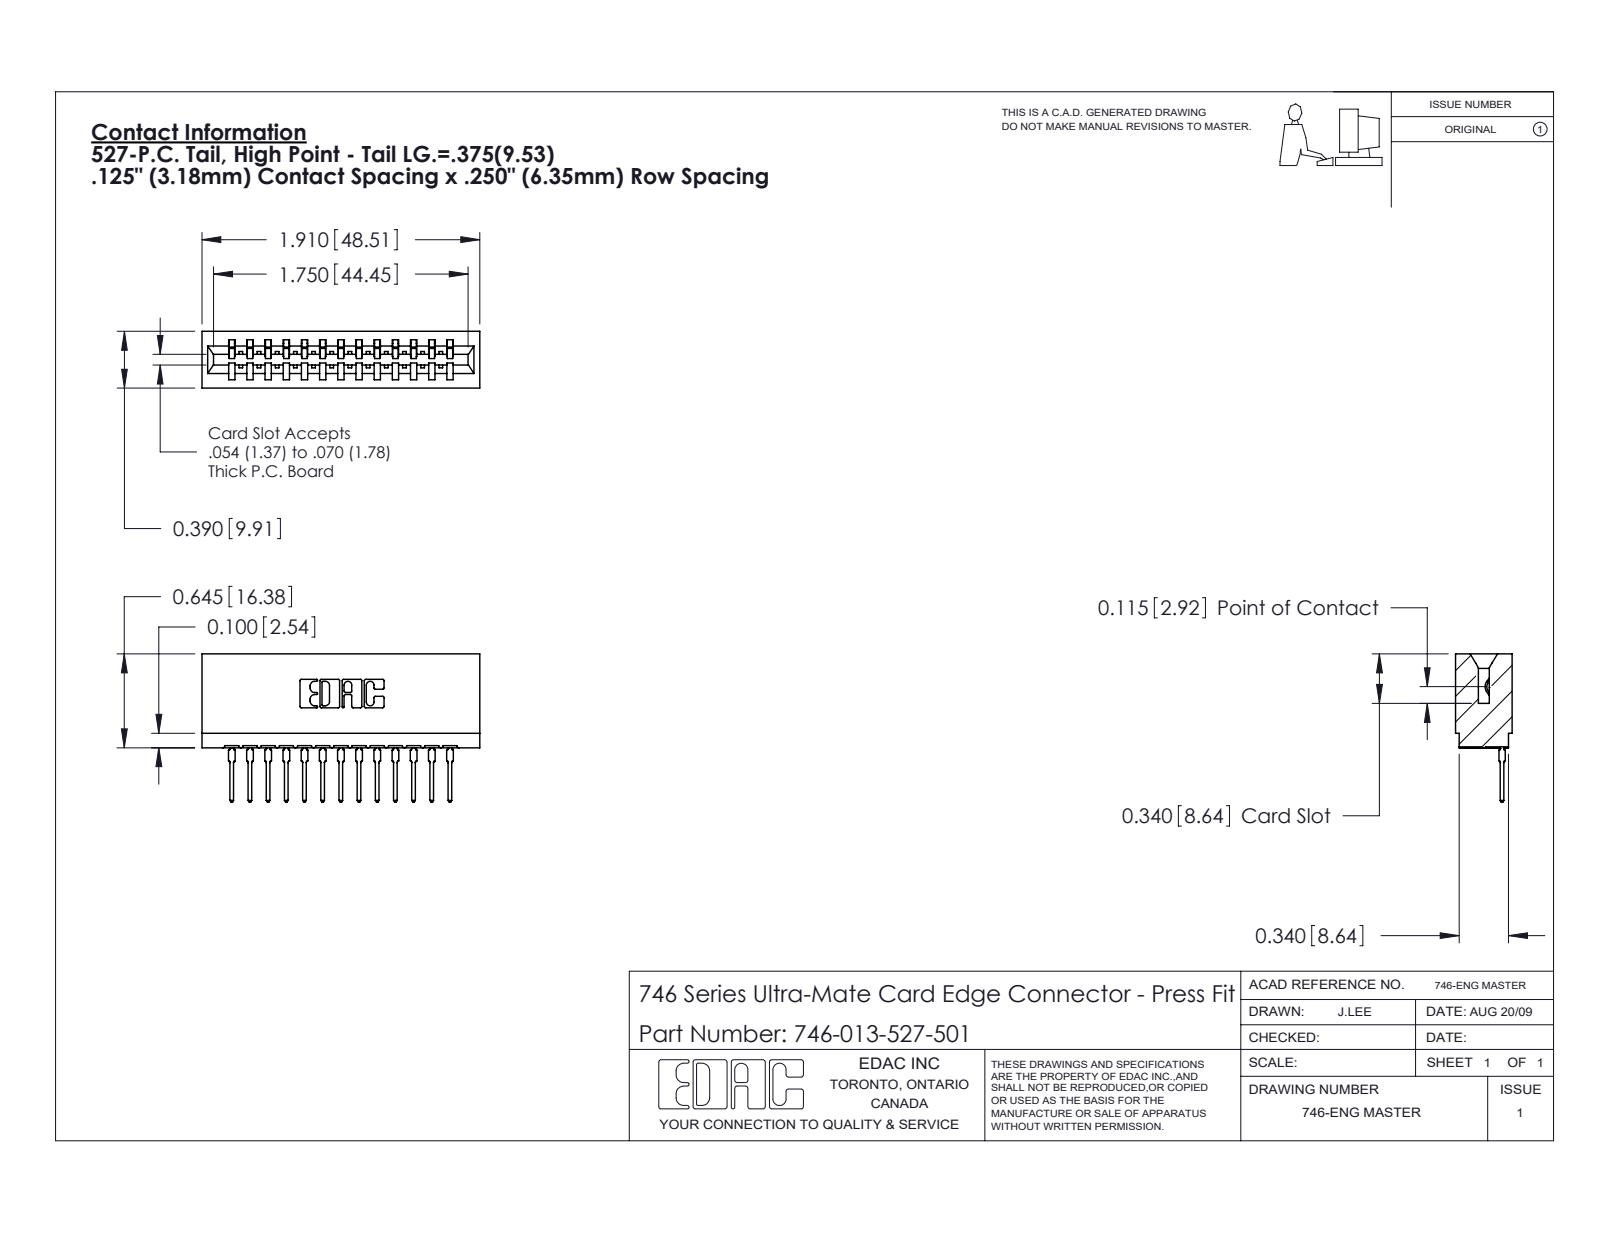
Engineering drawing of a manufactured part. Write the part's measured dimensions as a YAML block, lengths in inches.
part_name: "746-013-527-501; 746-292-001_527; 746 Part_.340 Slot Depth - 01"
step_written_by: "SolidWorks 2020 (CONFIG_CONTROL_DESIGN)"
units: inches
bodies: {solids: 14, faces: 1501, planar: 874, cylindrical: 289, other: 338}
overall_size: [1.91, 1.019, 0.39]
volume: 0.344
surface_area: 11.21
partial_cylinders:
  - {radius: 0.021, count: 26}
  - {radius: 0.01, count: 22}
  - {radius: 0.015, count: 14}
  - {radius: 0.007, count: 6}
  - {radius: 0.031, count: 6}
  - {radius: 0.005, count: 4}
  - {radius: 0.011, count: 4}
  - {radius: 0.026, count: 3}
face_to_face_distances: [0.25, 0.5, 0.333, 0.057, 0.125, 0.39, 0.042, 0.292, 0.75, 0.125]
